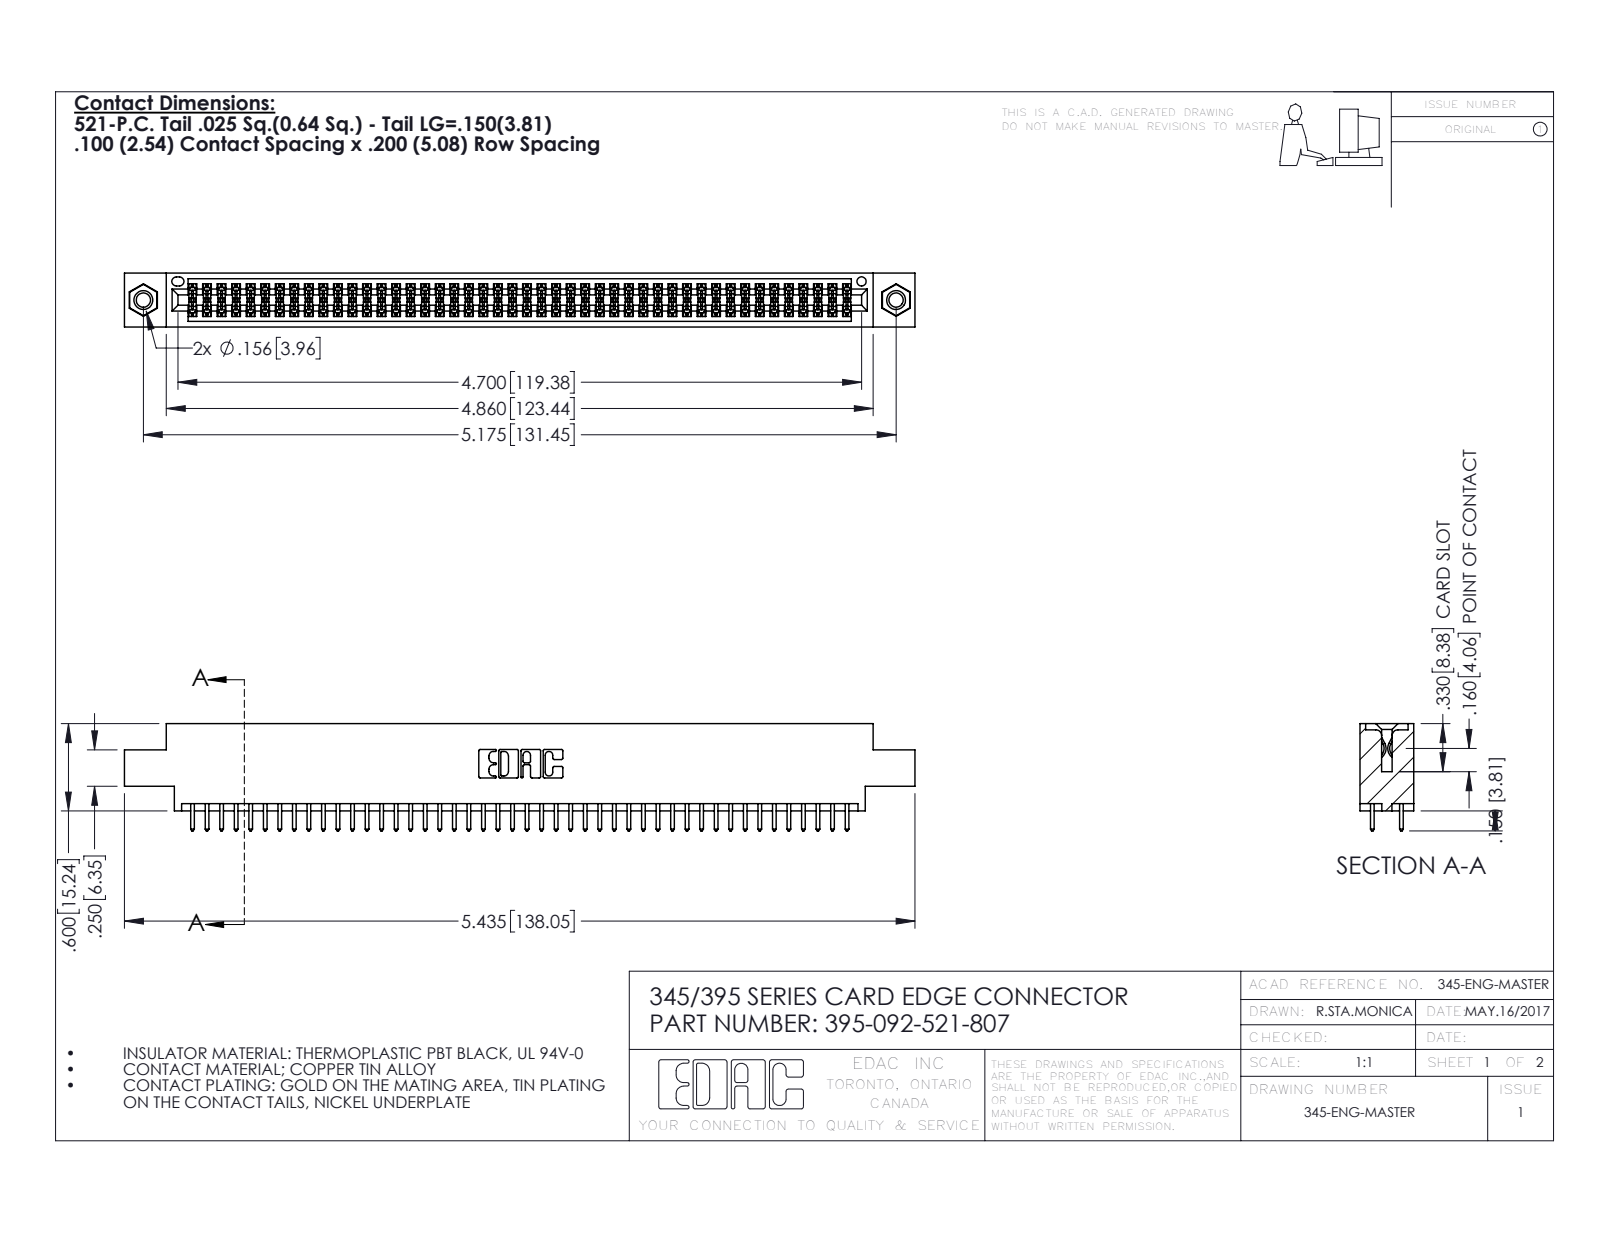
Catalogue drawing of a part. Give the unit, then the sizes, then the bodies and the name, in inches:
Units: inches
Overall size (bounding box): 5.435 × 0.737 × 0.37
Round holes (diameter × count): ⌀0.098 ×2, ⌀0.125 ×2, ⌀0.156 ×2, ⌀0.064 ×1
Round bosses / shafts (diameter × count): ⌀0.155 ×2
Partial cylindrical surfaces — rounded edges, fillets, slot ends (radius × count): R0.006 ×138, R0.01 ×92, R0.01 ×22, R0.007 ×6, R0.031 ×6, R0.026 ×3, R0.014 ×2, R0.019 ×2
Main face-to-face distances: 0.072, 0.298, 0.2, 0.37, 0.098, 0.272, 0.025, 0.225, 0.175, 0.149
Hole centre spacings: 0.27, 4.939, 5.175
Volume: 0.811 in³ · Surface area: 30.44 in²
Bodies: 95 solids, 4790 faces (3152 planar, 1622 cylindrical, 16 other)
Part name (STEP PRODUCT): 395-092-521-807; 345 Part_0.170 Offset - 0.156 Dia-TI; 345-250-001_345-250-005-103; 345-292-001_345-293-121
STEP written by: SolidWorks 2016 (CONFIG_CONTROL_DESIGN)
